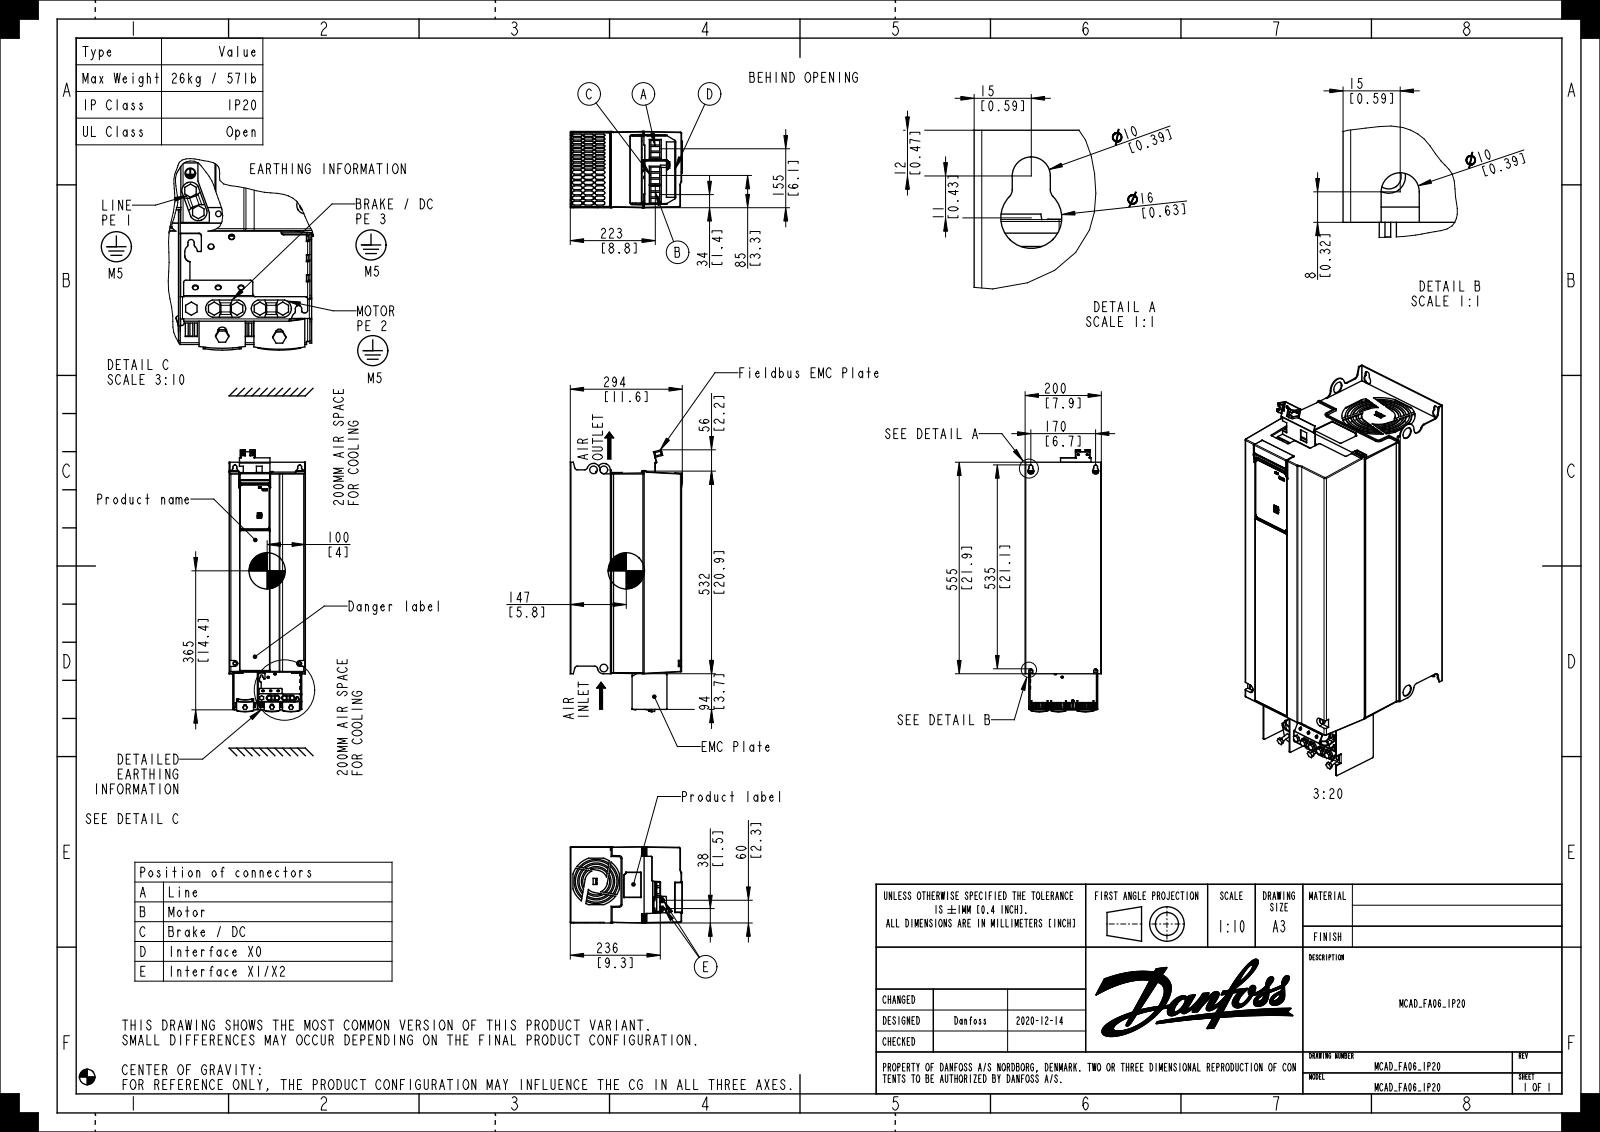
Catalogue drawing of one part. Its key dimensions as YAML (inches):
part_name: "FA06_SOLID_SW0003"
step_written_by: "CREO PARAMETRIC BY PTC INC, 2017260 (AUTOMOTIVE_DESIGN)"
units: inches
bodies: {solids: 1, faces: 2495, planar: 1614, cylindrical: 667, other: 214}
overall_size: [27.058, 11.575, 7.874]
volume: 1744
surface_area: 1423
round_holes:
  - {diameter: 0.197, count: 8}
  - {diameter: 0.256, count: 8}
  - {diameter: 0.344, count: 4}
  - {diameter: 0.787, count: 3}
  - {diameter: 0.177, count: 2}
  - {diameter: 0.236, count: 2}
  - {diameter: 0.163, count: 1}
  - {diameter: 0.365, count: 1}
  - {diameter: 2.795, count: 1}
  - {diameter: 3.543, count: 1}
  - {diameter: 4.291, count: 1}
  - {diameter: 5.039, count: 1}
round_bosses_or_shafts:
  - {diameter: 0.236, count: 9}
  - {diameter: 4.567, count: 1}
  - {diameter: 3.819, count: 1}
  - {diameter: 3.071, count: 1}
  - {diameter: 0.327, count: 1}
  - {diameter: 0.315, count: 1}
partial_cylinders:
  - {radius: 0.079, count: 77}
  - {radius: 0.118, count: 67}
  - {radius: 0.197, count: 62}
  - {radius: 0.02, count: 58}
  - {radius: 0.008, count: 36}
  - {radius: 0.059, count: 31}
  - {radius: 0.039, count: 22}
  - {radius: 0.012, count: 20}
face_to_face_distances: [0.059, 7.873, 7.874, 0.118, 11.378, 11.488, 0.11, 0.374, 11.496, 7.441]
hole_center_spacings: [0.787, 1.575, 3.267, 3.326, 1.299, 3.395, 3.562, 5.63]
